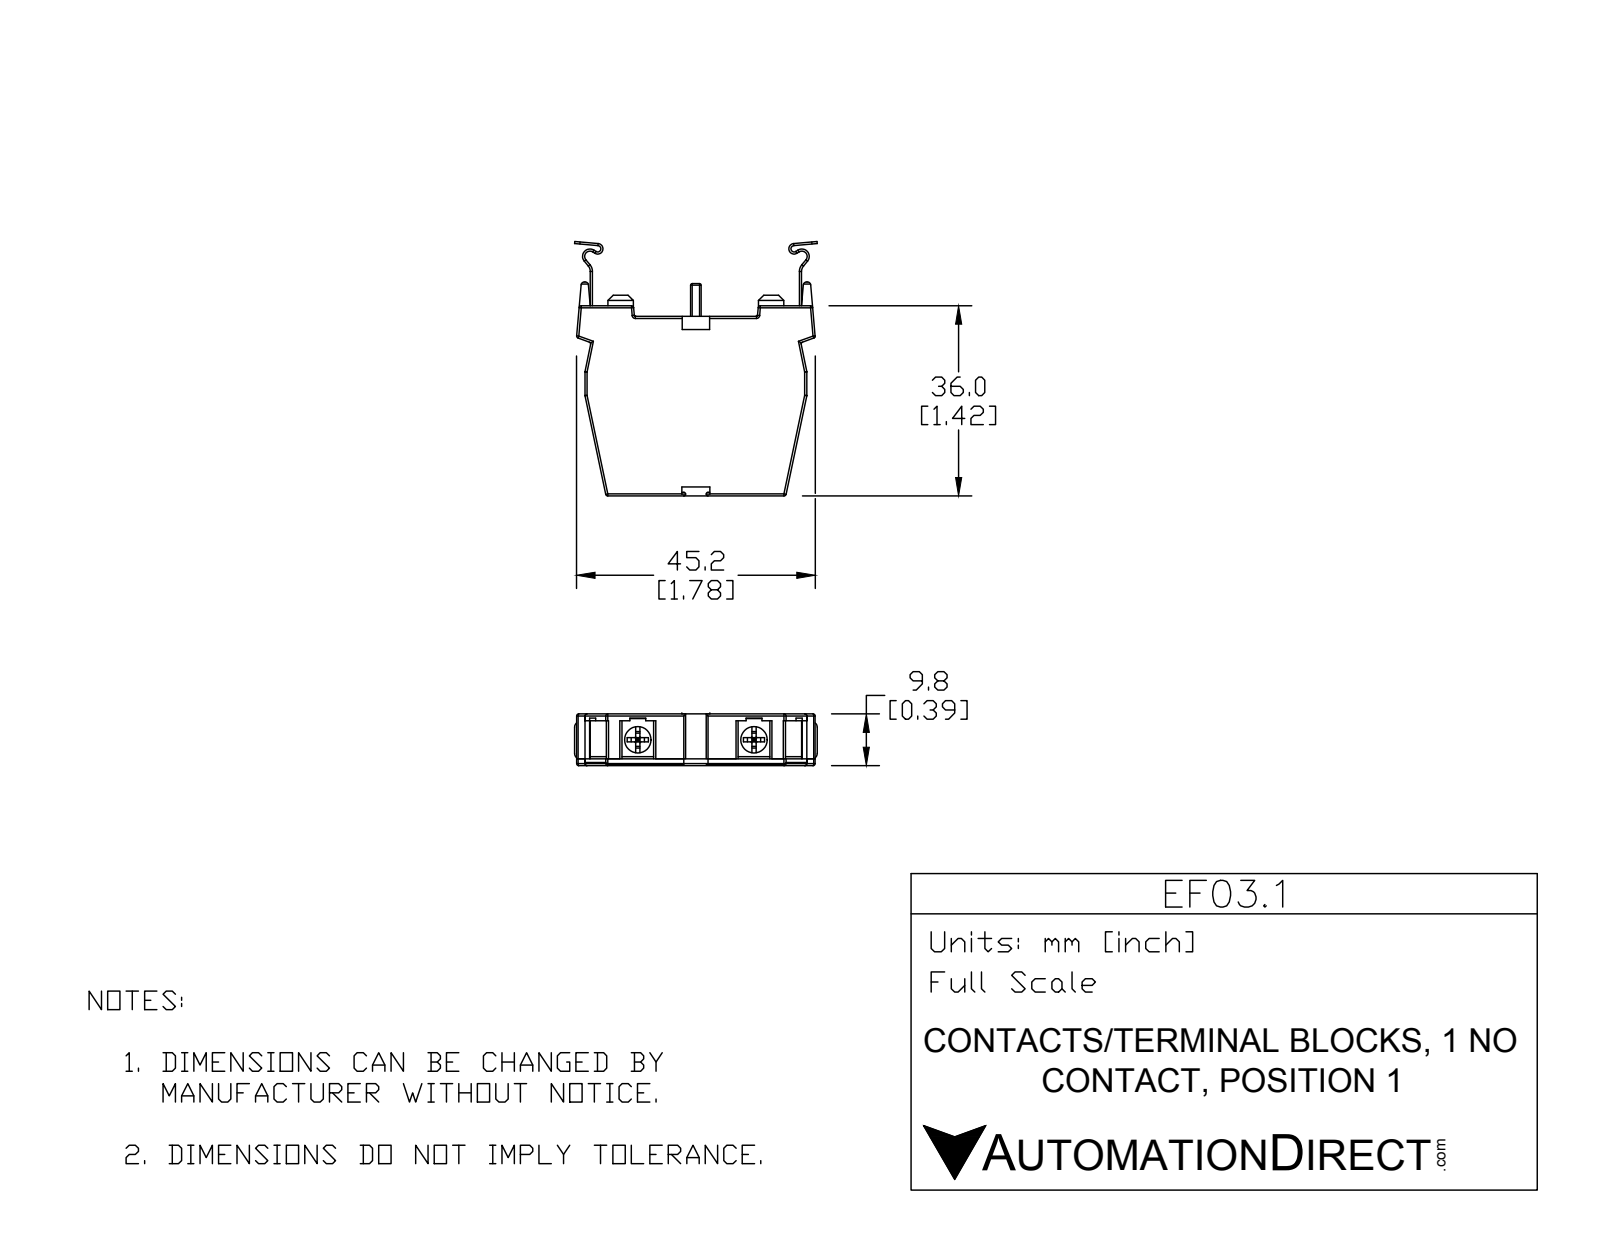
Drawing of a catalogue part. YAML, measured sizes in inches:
part_name: "EF03.1"
step_written_by: "SolidWorks 2015 (AUTOMOTIVE_DESIGN)"
units: inches
bodies: {solids: 7, faces: 277, planar: 155, cylindrical: 100, other: 22}
overall_size: [1.896, 1.822, 0.386]
volume: 0.742
surface_area: 10.33
round_holes:
  - {diameter: 0.197, count: 4}
round_bosses_or_shafts:
  - {diameter: 0.187, count: 2}
  - {diameter: 0.157, count: 2}
partial_cylinders:
  - {radius: 0.01, count: 44}
  - {radius: 0.02, count: 8}
  - {radius: 0.039, count: 6}
  - {radius: 0.024, count: 4}
  - {radius: 0.024, count: 2}
  - {radius: 0.039, count: 2}
  - {radius: 0.055, count: 2}
  - {radius: 0.063, count: 2}
face_to_face_distances: [0.386, 0.055, 0.331, 1.339, 0.276, 0.016, 0.079, 0.125, 1.464, 0.138]
hole_center_spacings: [0.859]
